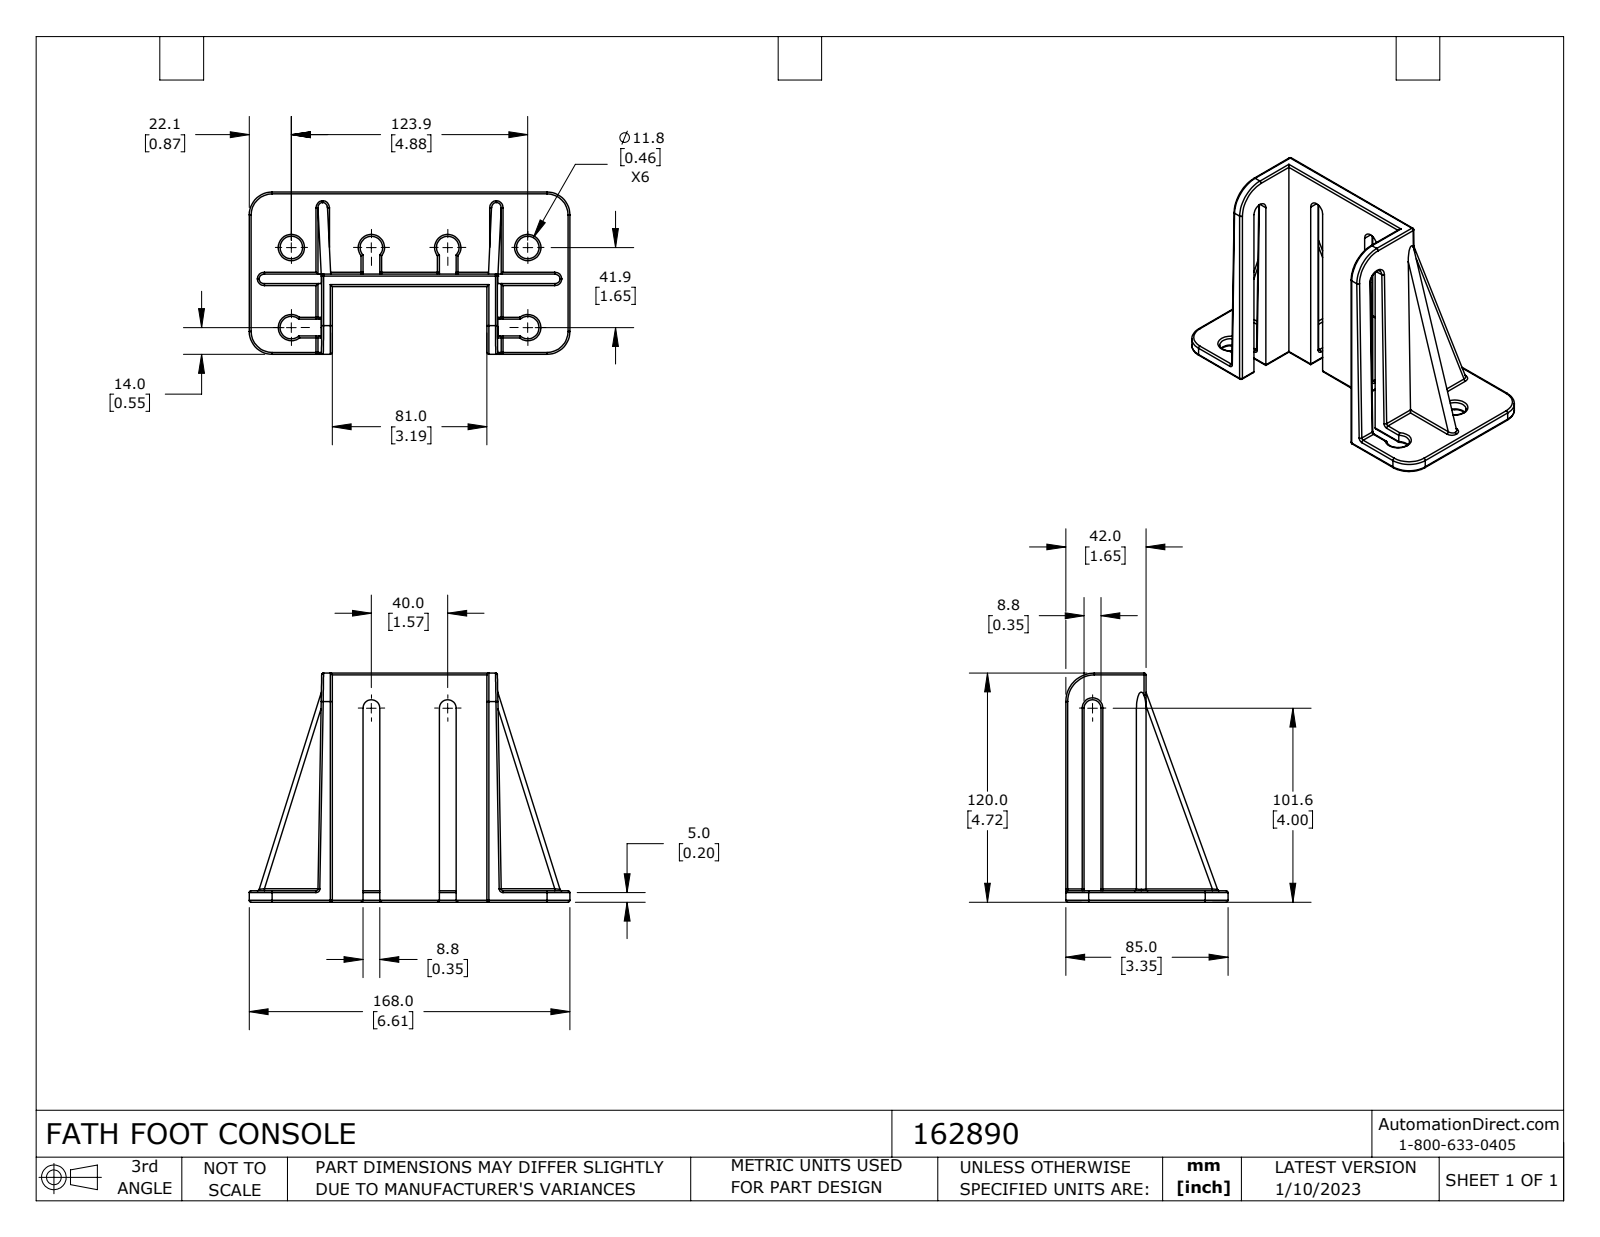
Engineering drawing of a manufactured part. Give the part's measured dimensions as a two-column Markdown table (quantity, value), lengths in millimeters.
| quantity | value |
| --- | --- |
| part name | 162890 |
| STEP written by | SolidWorks 2021 (CONFIG_CONTROL_DESIGN) |
| units | millimeters |
| bodies | 1 solid, 195 faces (30 planar, 97 cylindrical, 68 other) |
| overall size | 168 × 120 × 85 |
| volume | 193 200 mm³ |
| surface area | 73 810 mm² |
| round holes (diameter × count) | 11.8 × 2 |
| partial cylindrical surfaces (radius × count) | 1 × 49, 2.5 × 4, 5.9 × 4, 12 × 4, 4.4 × 3, 15 × 1 |
| main face-to-face distances | 6.5, 6, 5, 81, 1.5, 8.8, 25.9, 27.4, 32.4, 17.1 |
| hole center spacings | 123.9 |
